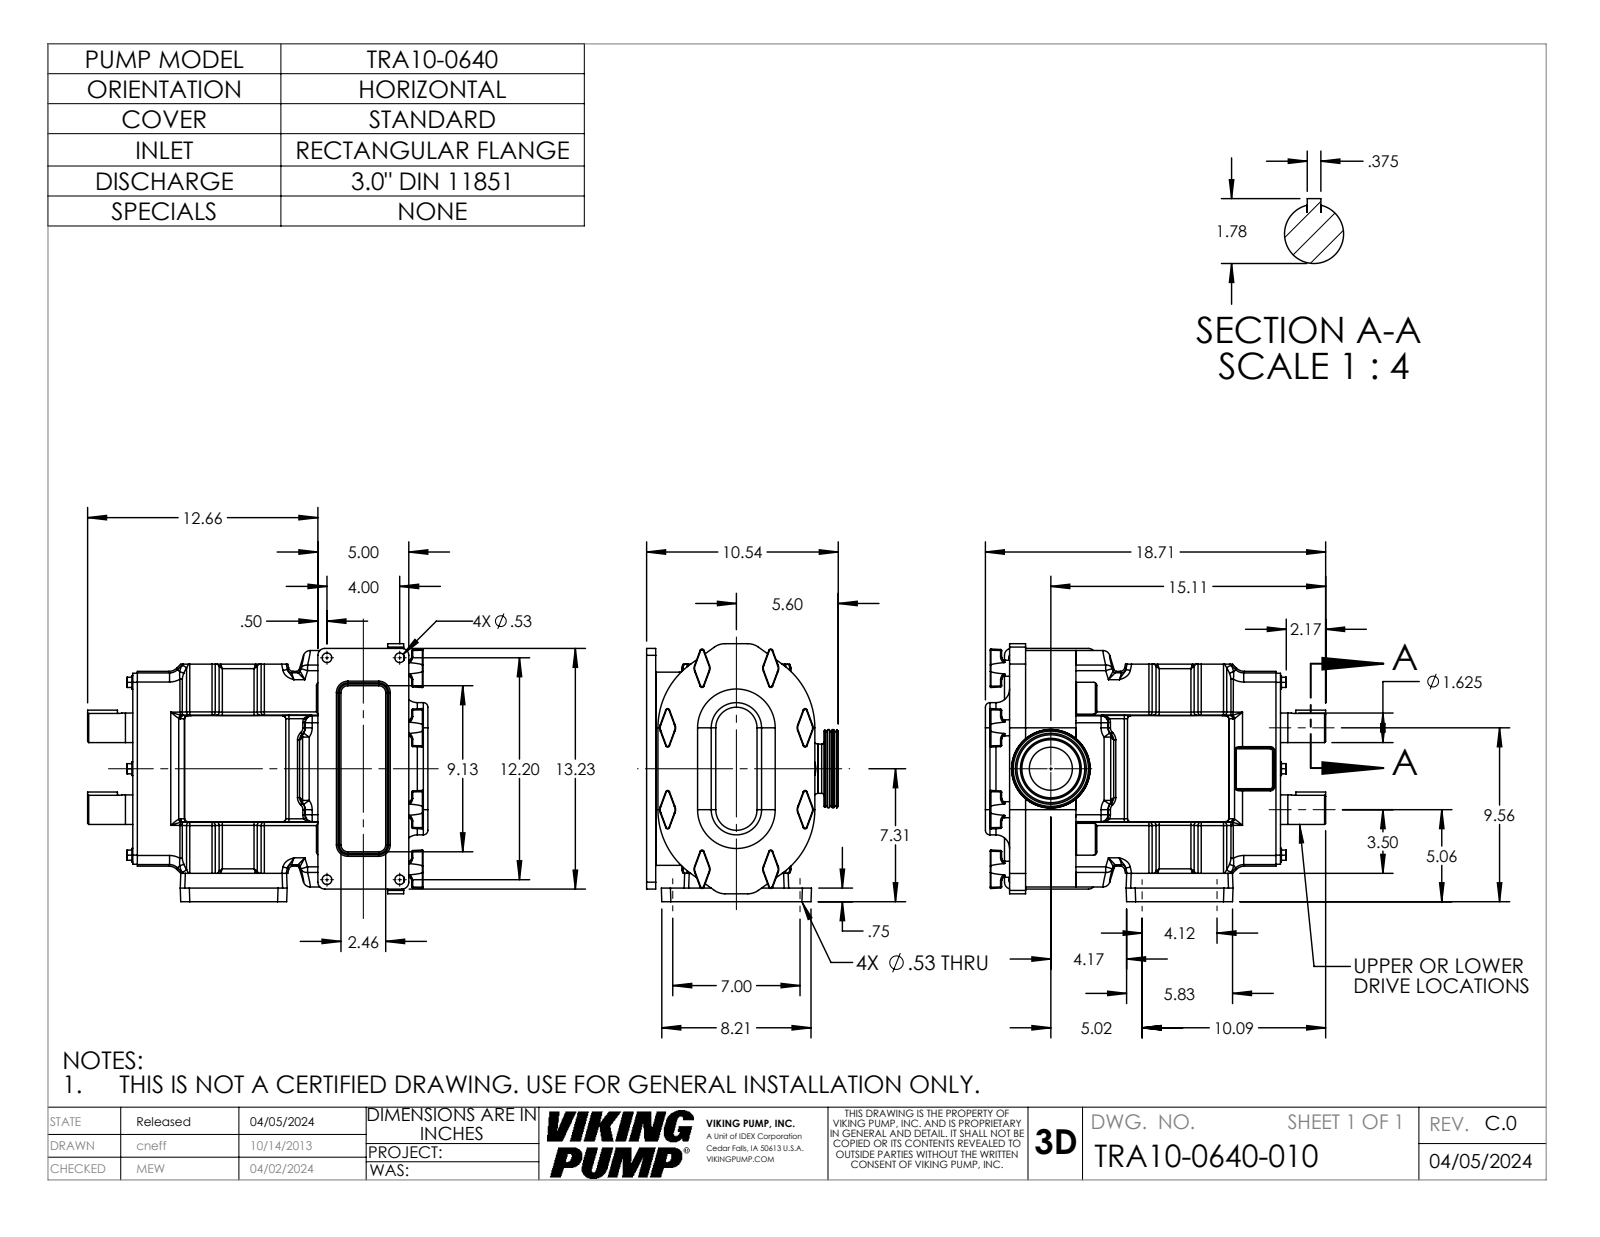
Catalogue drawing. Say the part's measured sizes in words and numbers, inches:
The part is named "TRA10-0600-COVER-STD; TRA10-0640-010; 0600DIN11851-30; TRA10-0640-BODY (+1 more)". Its 3-D file was written by "SolidWorks 2022 (AUTOMOTIVE_DESIGN)". It is 4 solids with 1106 faces: 297 planar, 393 cylindrical and 416 other. Overall it measures 18.714 by 14.185 by 10.539 inches. Its volume is 1 231 cubic inches and its surface area 1 453 square inches. Round holes: 8 of diameter 0.531, 1 of diameter 2.368, 1 of diameter 3.732. Round bosses or shafts: 8 of diameter 0.88, 6 of diameter 0.75, 2 of diameter 1.624, 1 of diameter 3.346, 1 of diameter 2.708. Partial cylindrical surfaces (rounded edges, fillets, slot ends): 44 of radius 0.18, 43 of radius 0.06, 36 of radius 0.03, 36 of radius 0.38, 32 of radius 0.25, 24 of radius 0.12, 22 of radius 0.5, 16 of radius 0.09. The main face-to-face distances are 2.769, 0.5, 1.437, 0.88, 3.649, 7.937, 0.36, 11.25, 14.899, 14.019. The hole center spacings are 4, 4.12, 6.404, 6.435, 7, 8.122, 12.2, 12.839.
